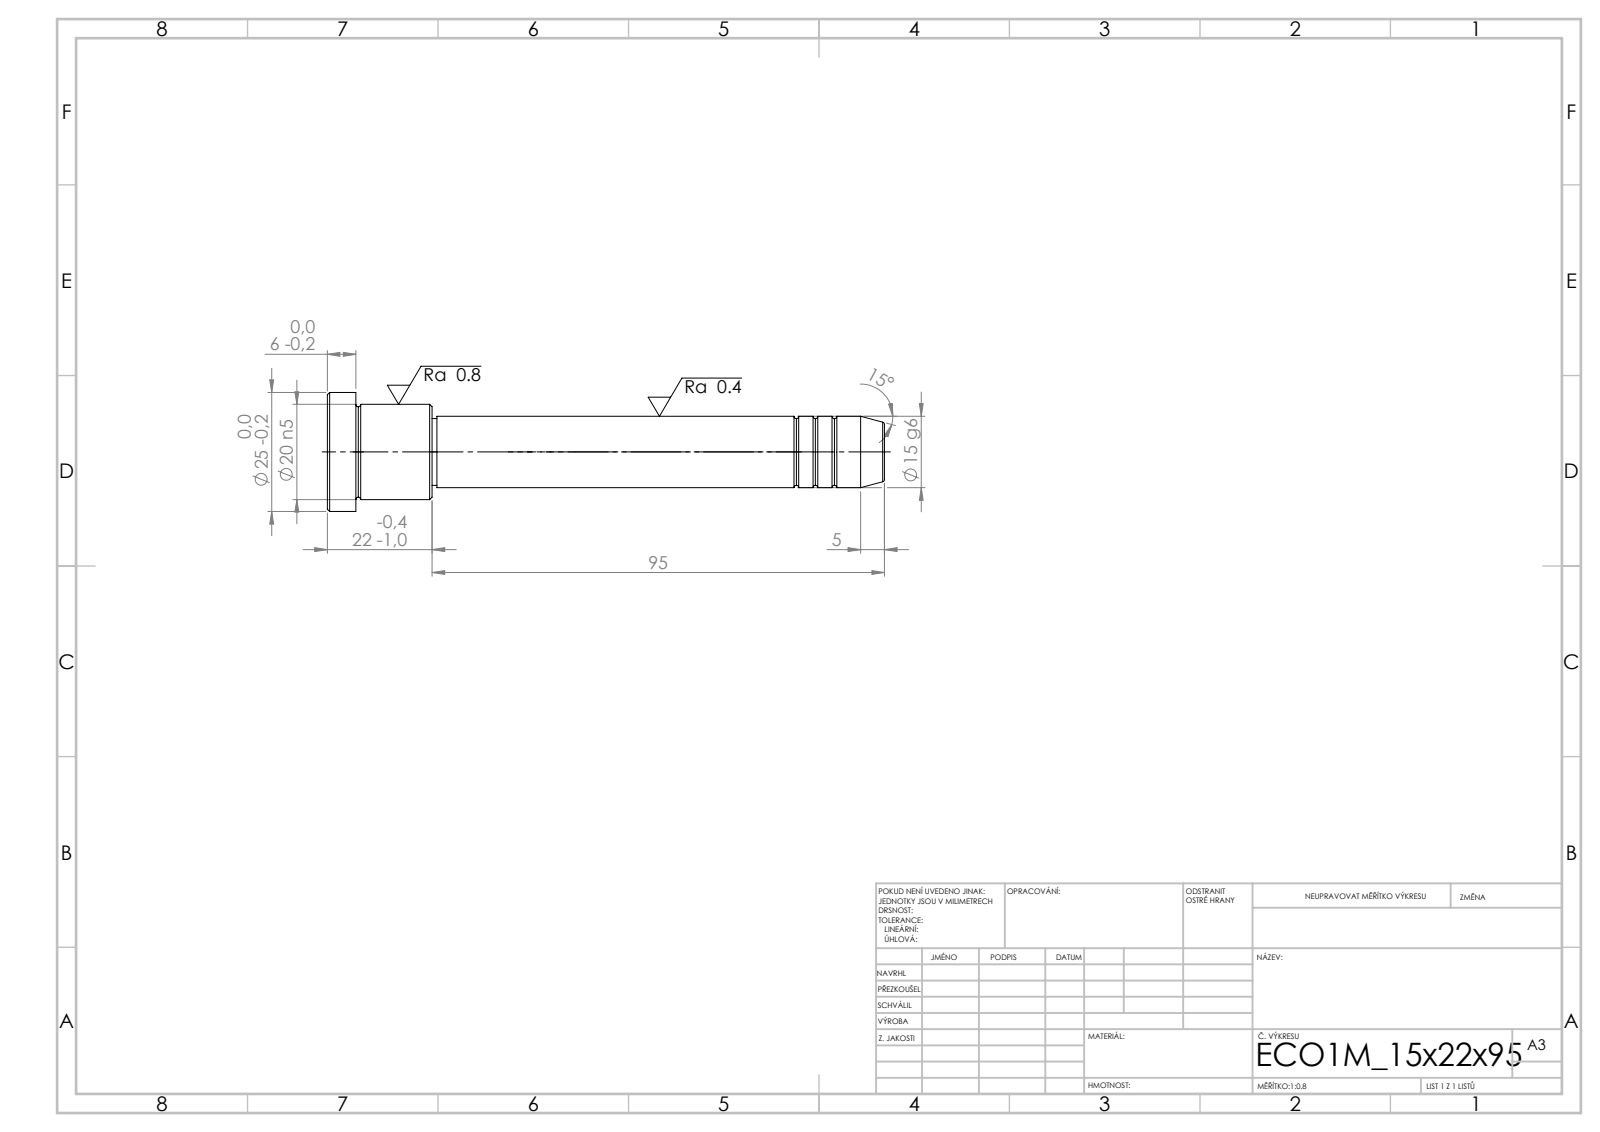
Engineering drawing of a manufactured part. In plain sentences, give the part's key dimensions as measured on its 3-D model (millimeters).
Its 3-D file was written by "SolidWorks 2019 (CONFIG_CONTROL_DESIGN)". It is 1 solid with 43 faces: 5 planar, 14 cylindrical and 24 other. Overall it measures 117 by 25 by 25 millimeters. Its volume is 24 492 cubic millimeters and its surface area 6 964 square millimeters. Round bosses or shafts: 1 of diameter 25, 1 of diameter 20, 1 of diameter 15, 1 of diameter 14. The main face-to-face distances are 6, 16, 22, 95, 111, 117, 94, 1, 17, 23.
